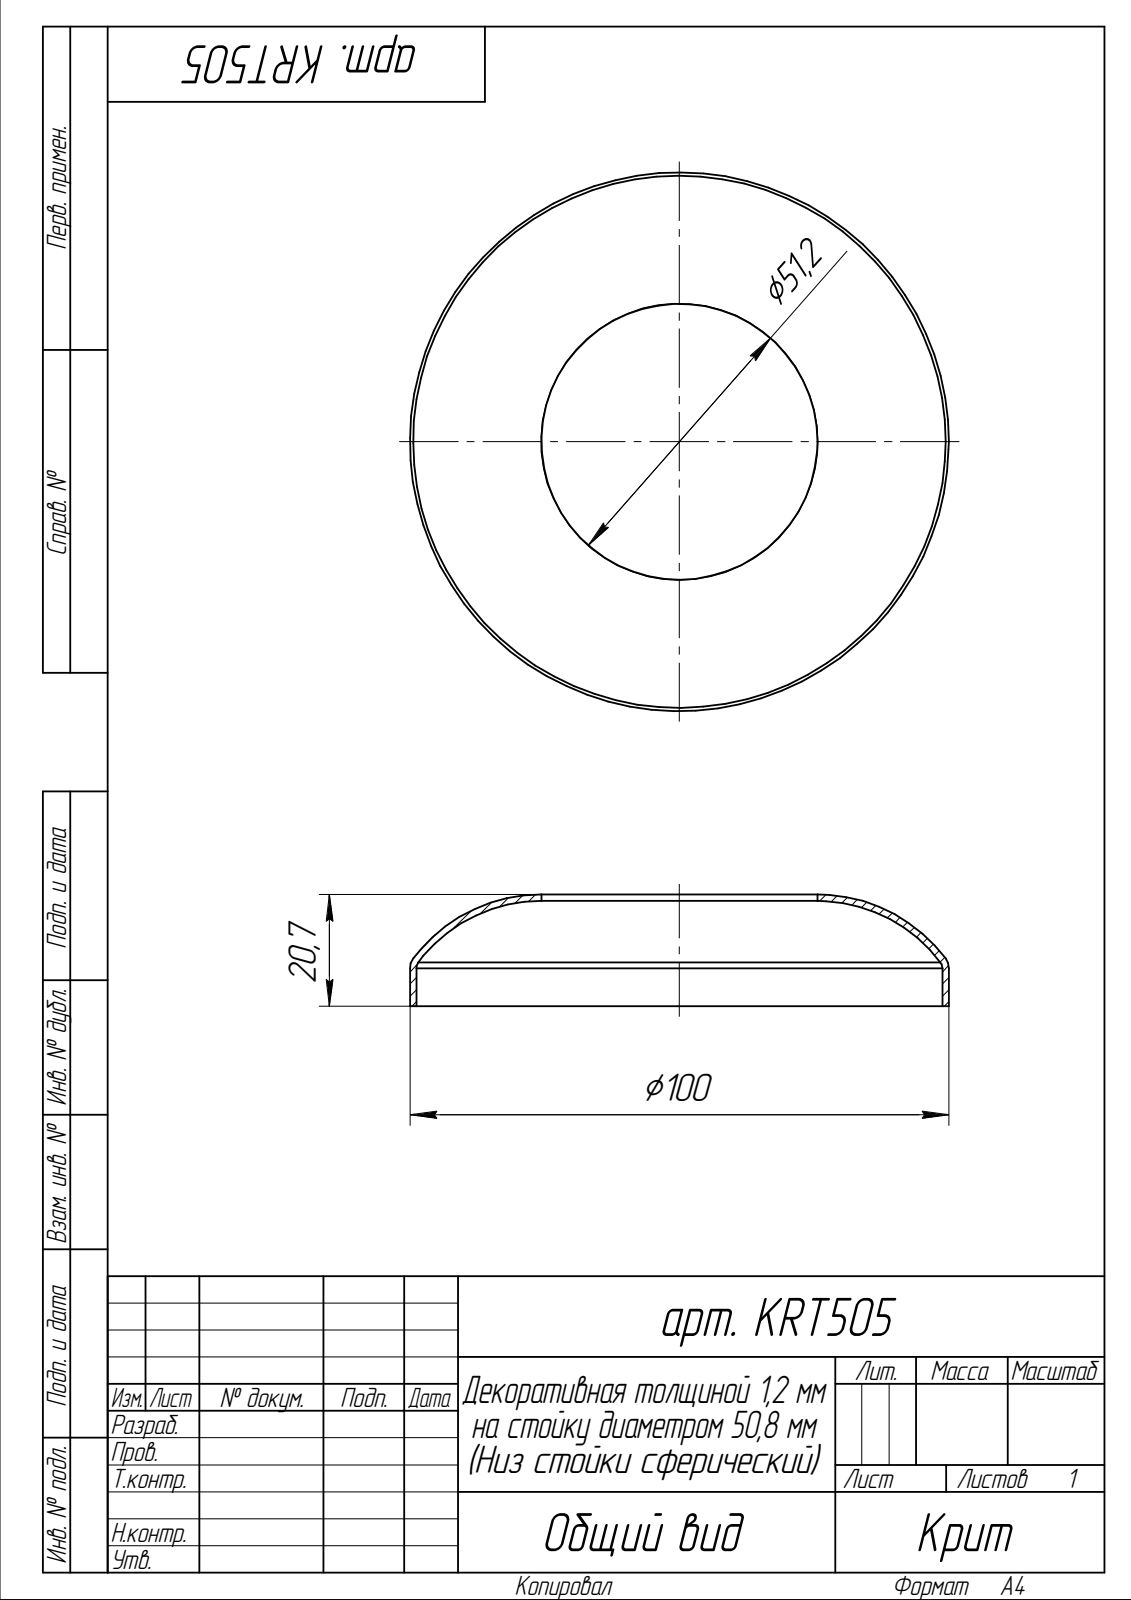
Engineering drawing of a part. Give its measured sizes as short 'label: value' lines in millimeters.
name: арт. KRT505
written by: SolidWorks 2014 (AUTOMOTIVE_DESIGN)
unit: mm
bodies: 1 solid, 17 faces (3 planar, 6 cylindrical, 8 other)
size: 100 × 100 × 20.7
volume: 10 973 mm³; area: 18 856 mm²
holes: 1× ⌀51.2, 1× ⌀97.6
bosses: 1× ⌀100
face distances: 19.5, 20.7, 1.2
